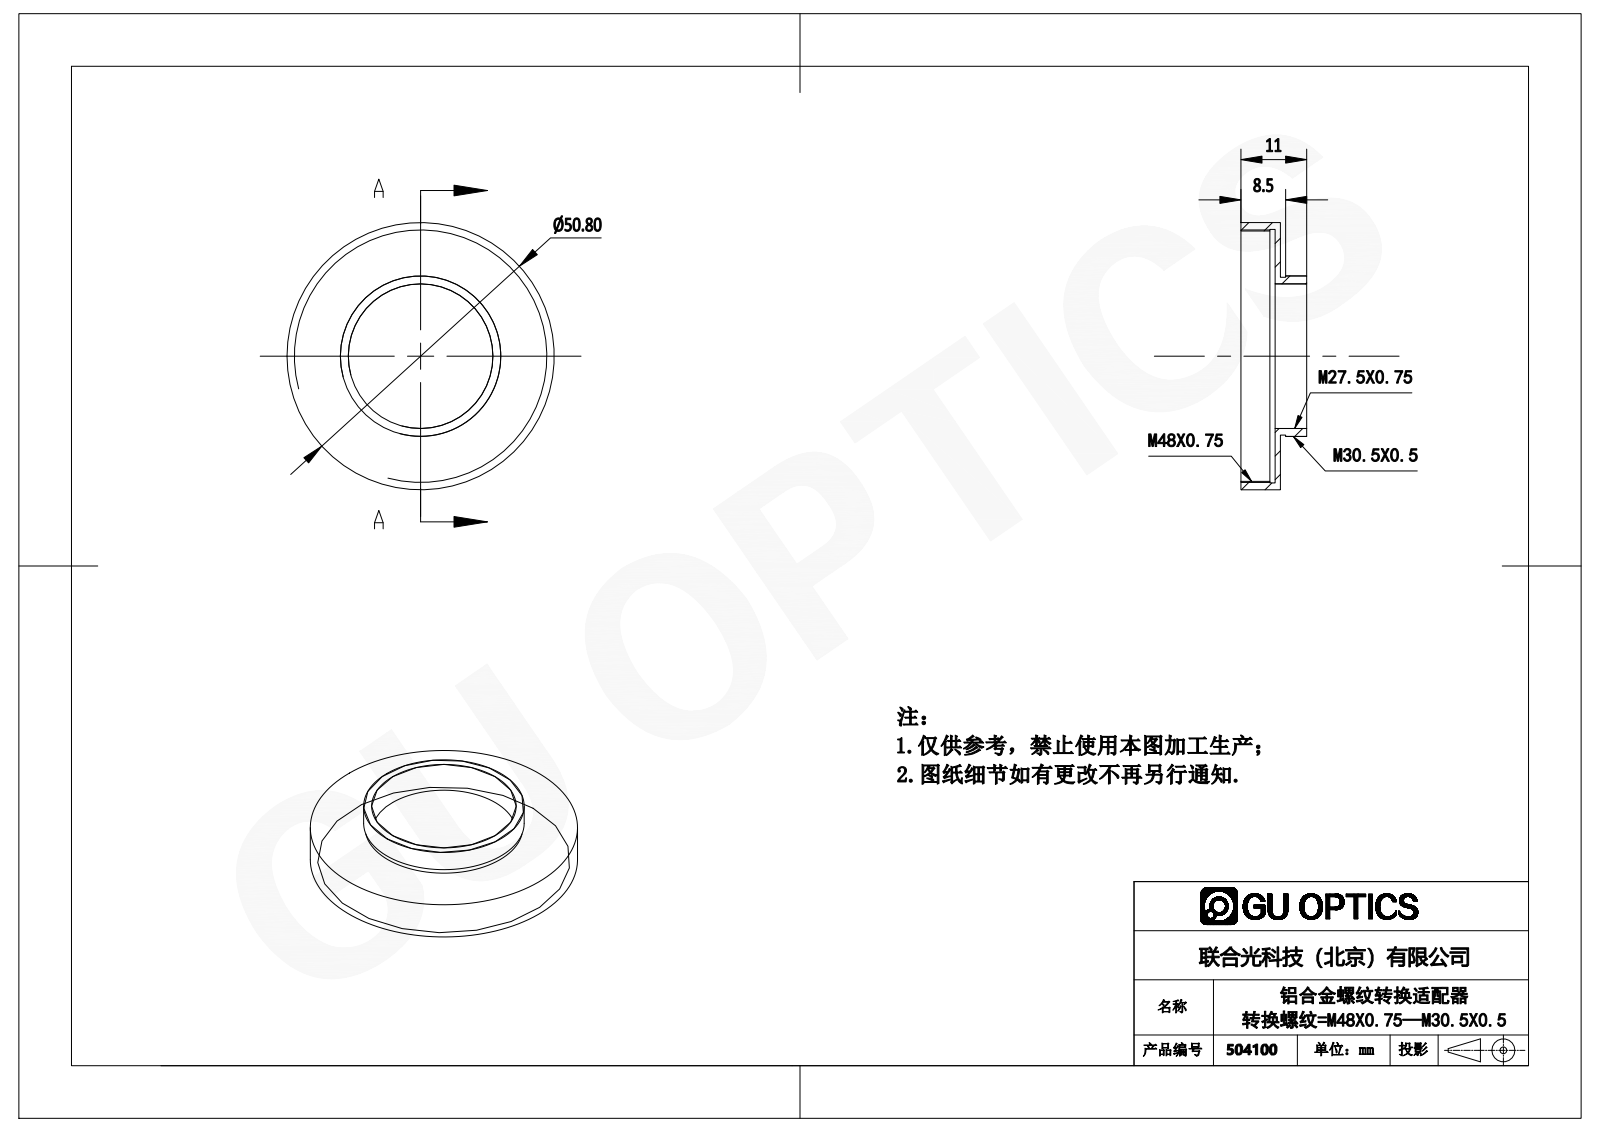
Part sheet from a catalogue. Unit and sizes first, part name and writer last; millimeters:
Units: millimetres
Overall size (bounding box): 50.8 × 50.8 × 11
Round holes (diameter × count): ⌀27.48 ×1, ⌀47.6 ×1, ⌀48.2 ×1
Round bosses / shafts (diameter × count): ⌀50.8 ×1, ⌀30.52 ×1, ⌀30 ×1
Main face-to-face distances: 2, 5.5, 7.5, 11, 3.5, 1, 3, 4.5, 6.5, 8.5
Volume: 4 642 mm³ · Surface area: 5 837 mm²
Bodies: 1 solid, 18 faces (6 planar, 12 cylindrical, 0 other)
Part name (STEP PRODUCT): 504100
STEP written by: SolidWorks 2016 (AUTOMOTIVE_DESIGN)
